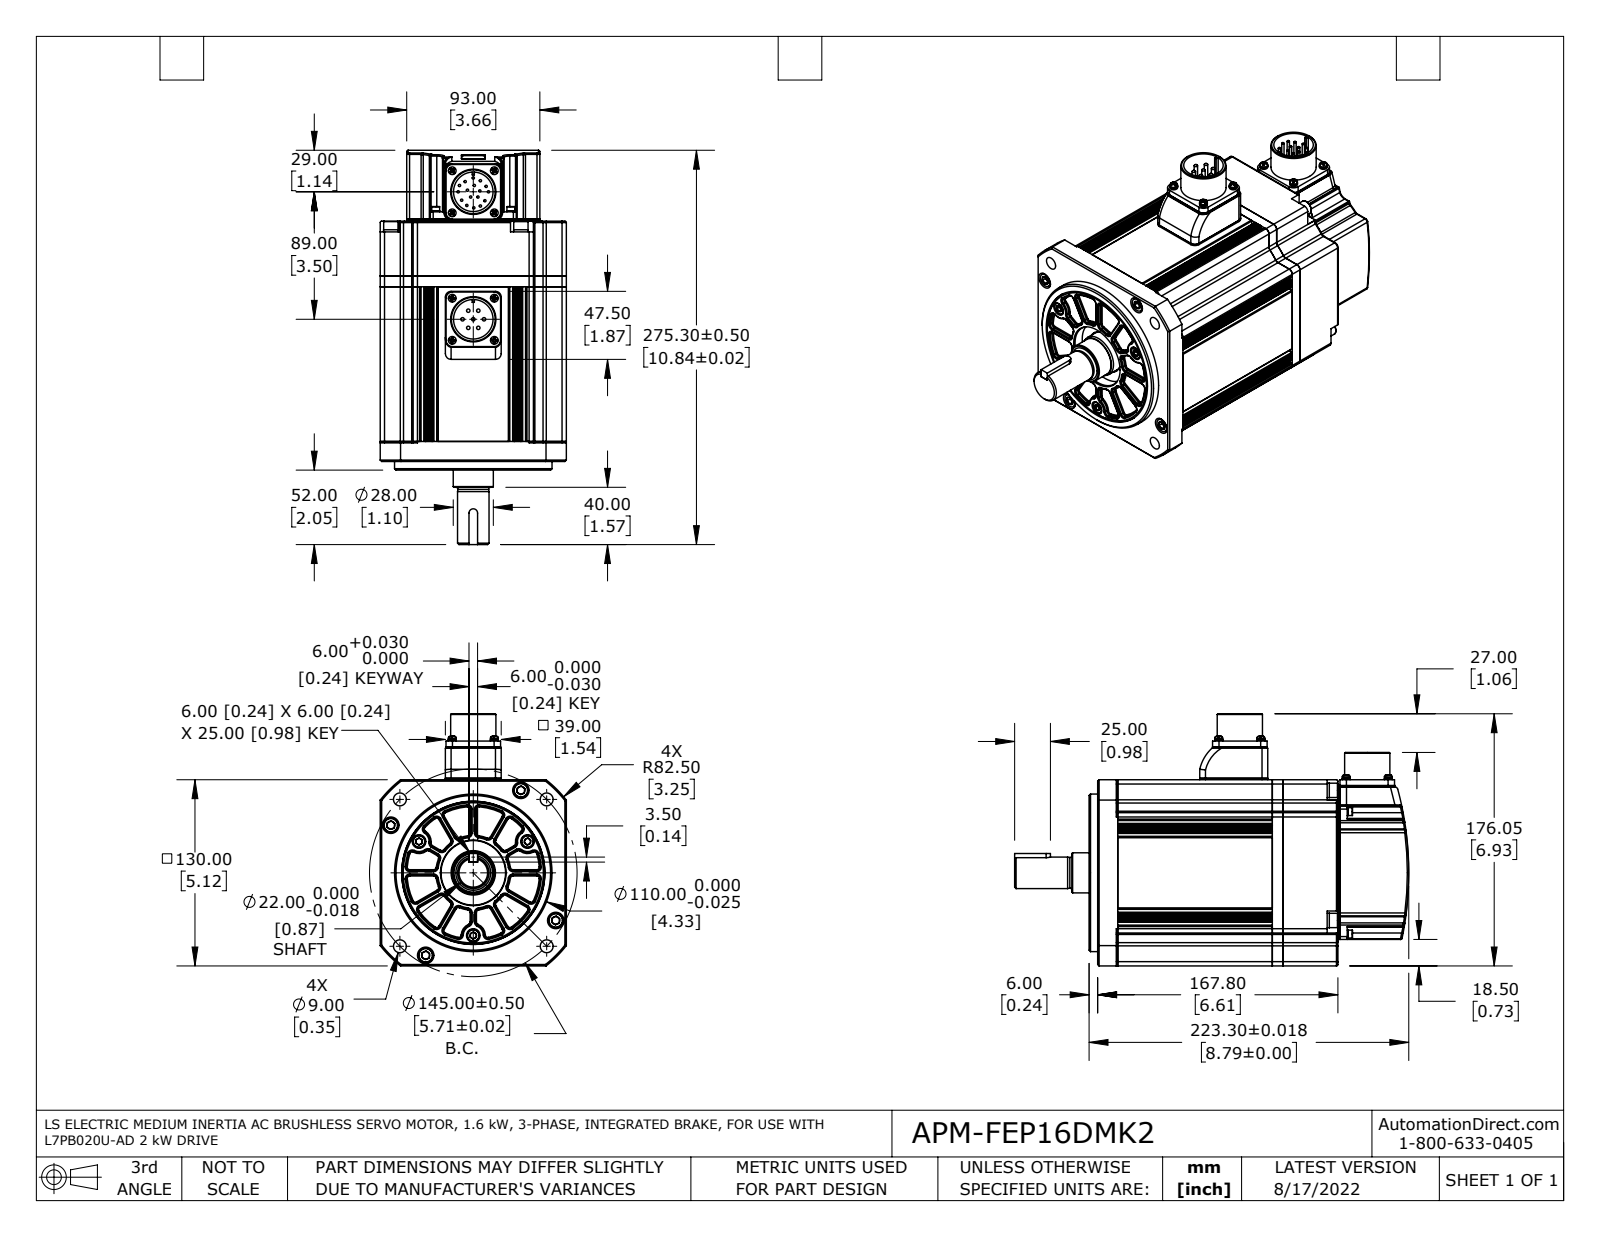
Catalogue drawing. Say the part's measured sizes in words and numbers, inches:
The part is named "FMP13GA003G03_Out Line(APM-FEP16D_K2) r1 nc fxt". Its 3-D file was written by "SolidWorks 2017 (AUTOMOTIVE_DESIGN)". It is 57 solids with 2214 faces: 729 planar, 843 cylindrical and 642 other. Overall it measures 10.839 by 6.931 by 5.118 inches. Its volume is 182.5 cubic inches and its surface area 550.4 square inches. Round holes: 12 of diameter 0.098, 8 of diameter 0.118, 8 of diameter 0.12, 8 of diameter 0.138, 7 of diameter 0.197, 4 of diameter 0.142, 4 of diameter 0.146, 4 of diameter 0.268, 4 of diameter 0.276, 4 of diameter 0.354, 4 of diameter 0.453, 3 of diameter 0.22. Round bosses or shafts: 17 of diameter 0.063, 8 of diameter 0.213, 7 of diameter 0.094, 4 of diameter 0.402, 4 of diameter 0.394, 4 of diameter 0.236, 4 of diameter 0.217, 4 of diameter 0.118. Partial cylindrical surfaces (rounded edges, fillets, slot ends): 72 of radius 0.02, 54 of radius 0.098, 24 of radius 0.028, 22 of radius 0.039, 17 of radius 0.079, 17 of radius 0.118, 12 of radius 0.177, 8 of radius 0.157. The main face-to-face distances are 4.252, 0.299, 4.551, 0.039, 5.118, 6.114, 0.906, 1.524, 1.823, 6.075. The hole center spacings are 0.819, 1.157, 3.504, 0.752, 1.041, 1.637, 1.975, 2.618.
